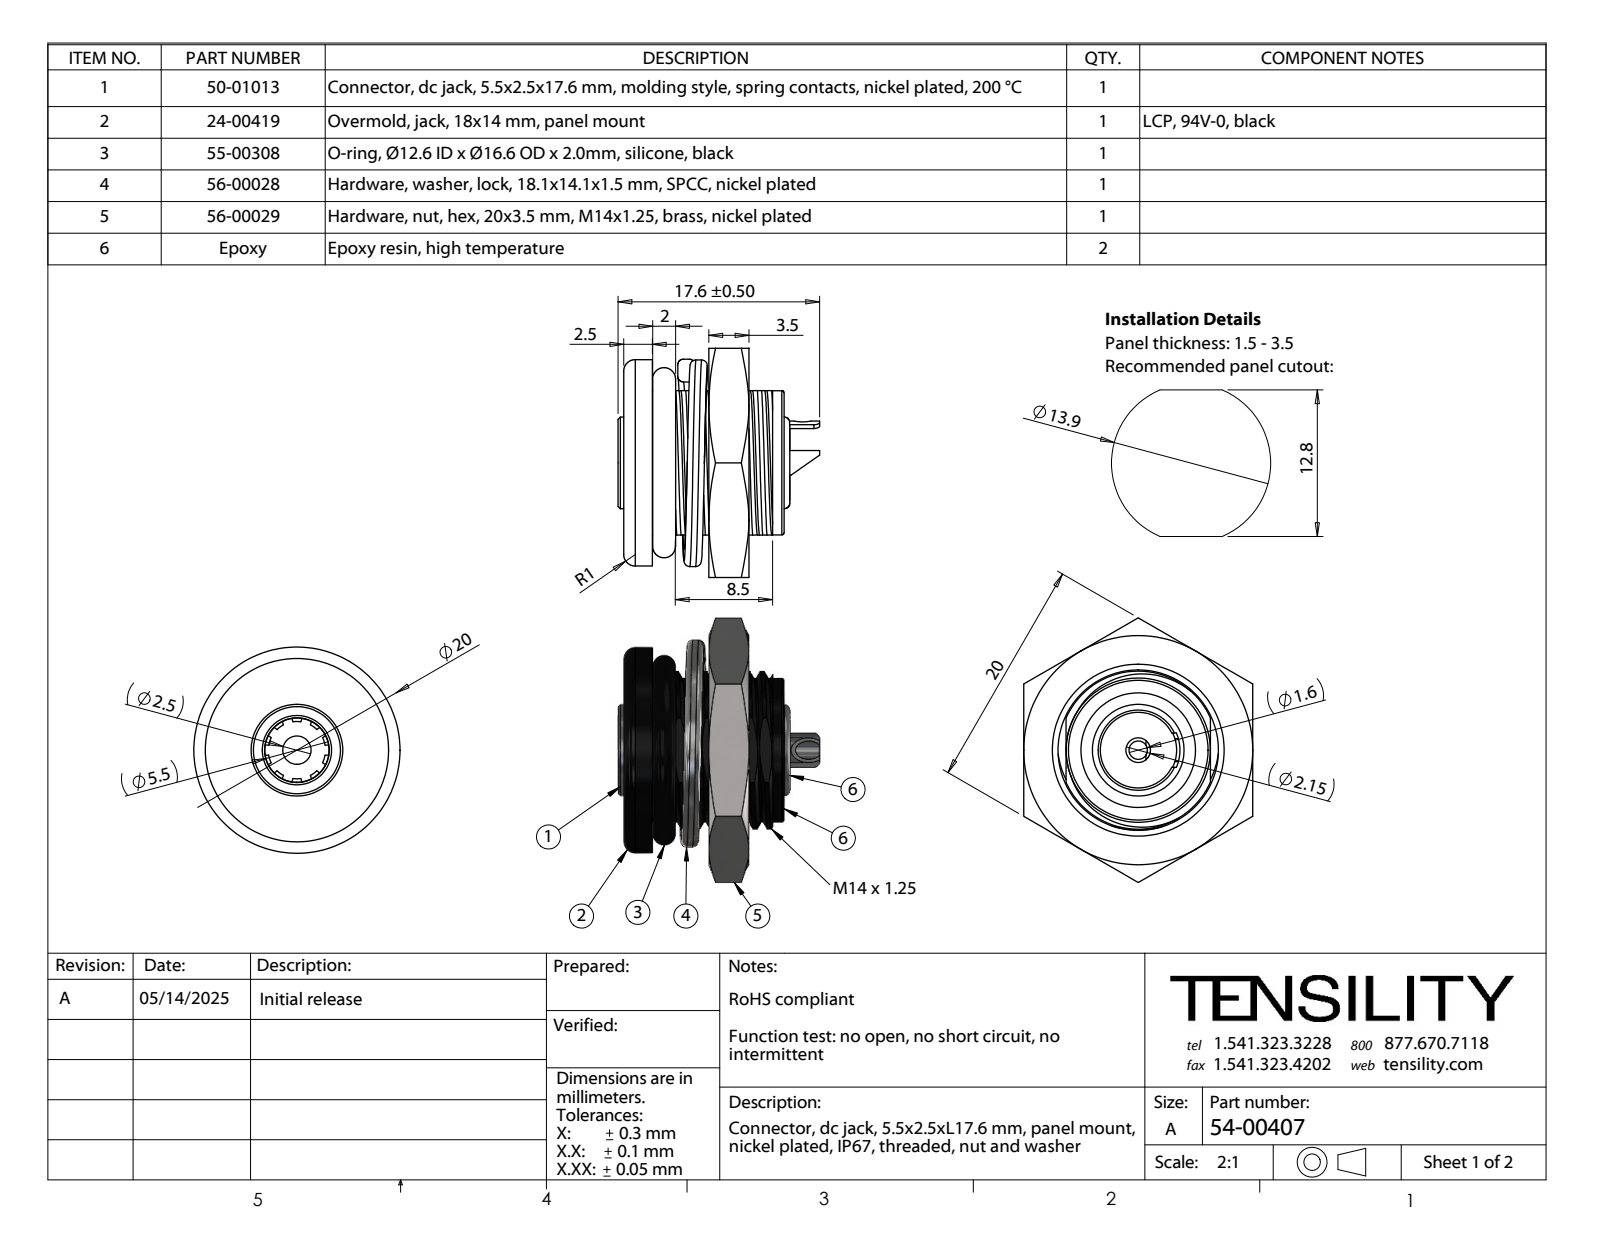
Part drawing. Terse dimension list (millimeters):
name: 54-00407; 50-01013 center pin_Center pin; 50-01013 shell_Shell; 56-00029 (+6 more)
written by: SolidWorks 2021 (AUTOMOTIVE_DESIGN)
unit: mm
bodies: 8 solids, 286 faces (100 planar, 79 cylindrical, 107 other)
size: 23.09 × 20 × 17.6
volume: 2 820 mm³; area: 4 248 mm²
holes: 2× ⌀1.5, 1× ⌀1.6, 1× ⌀2.15, 1× ⌀2.47, 1× ⌀5.6, 1× ⌀5.65, 1× ⌀6.4, 1× ⌀6.6, 1× ⌀7.6, 1× ⌀8, 1× ⌀10, 1× ⌀14
bosses: 1× ⌀18, 1× ⌀12.6, 1× ⌀12.59, 1× ⌀7.3, 1× ⌀6.2
rounds: 2× R0.5, 1× R3.35, 1× R6.9
face distances: 3.5, 10.93, 7.43, 4.93, 2.5, 8.43, 20, 3.7, 16.3, 8.5
